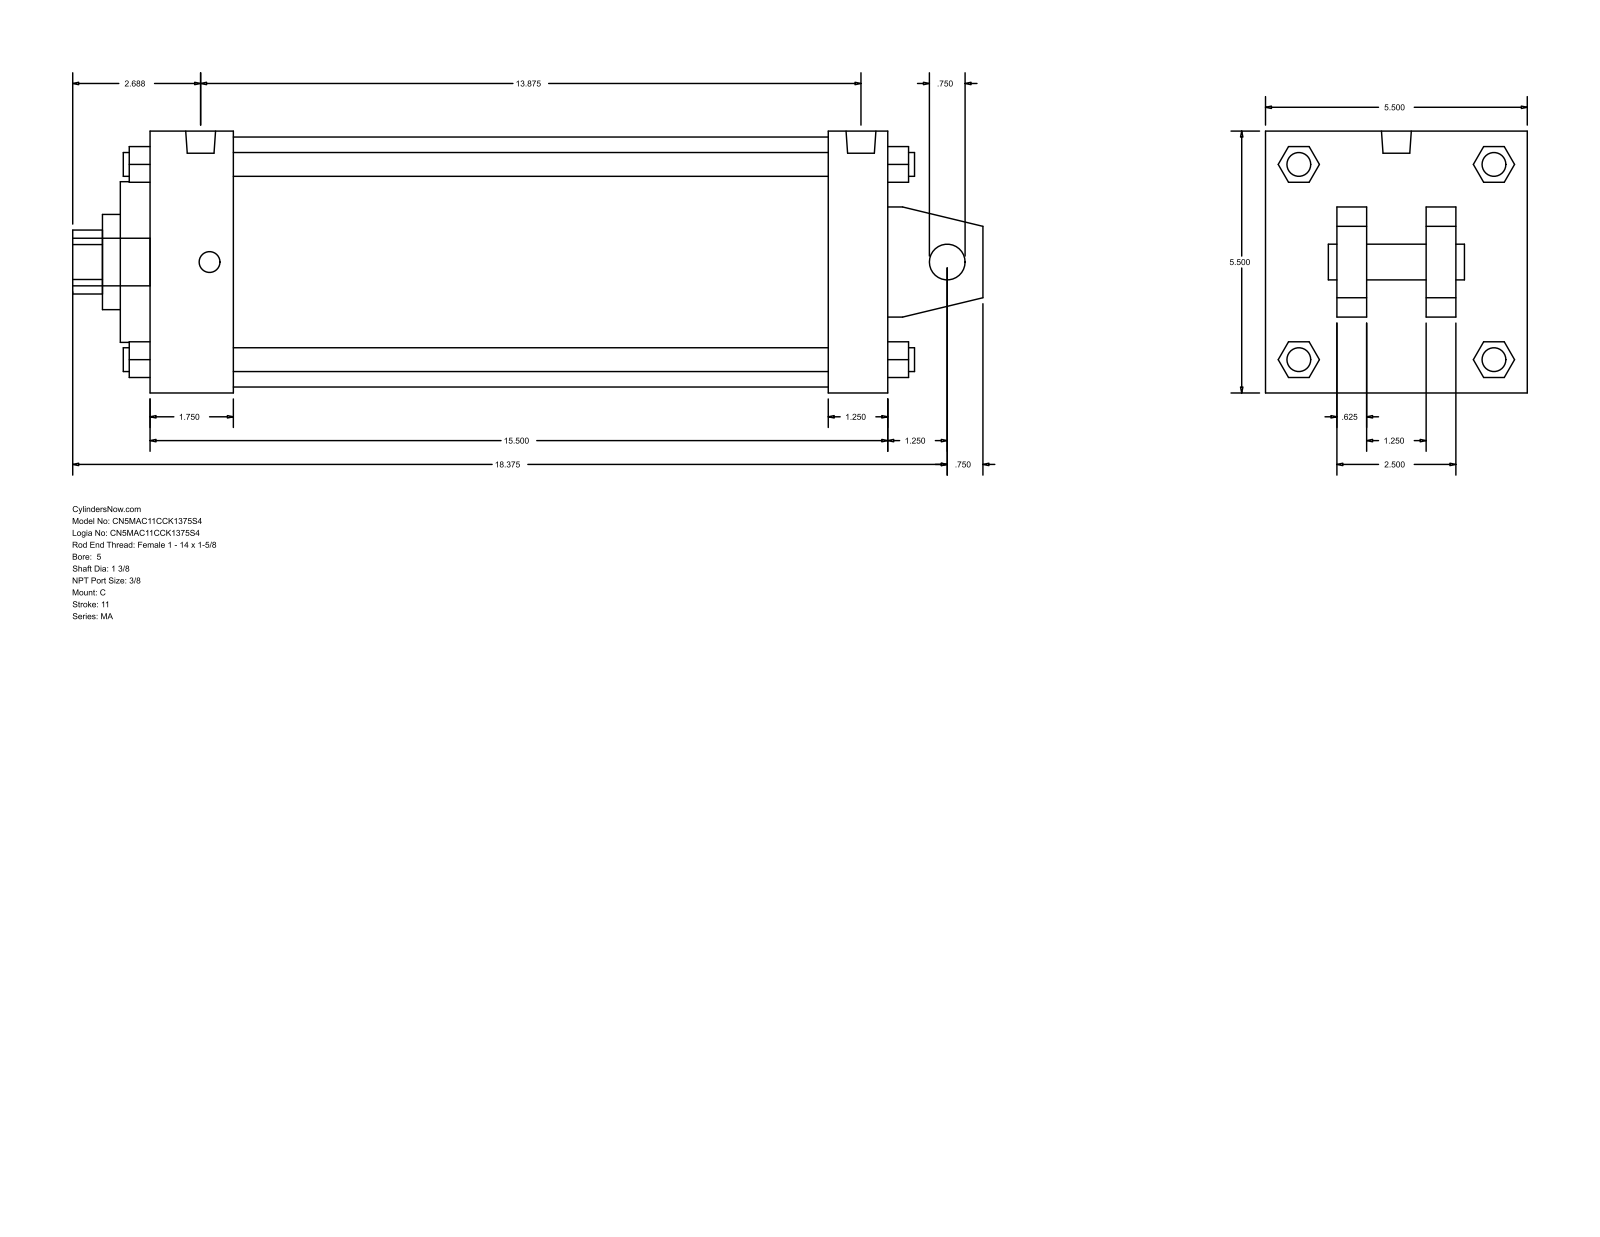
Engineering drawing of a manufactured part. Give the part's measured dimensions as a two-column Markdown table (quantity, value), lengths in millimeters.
| quantity | value |
| --- | --- |
| part name | MA_C__0500_1.375 |
| STEP written by | GSSL Pune (CONFIG_CONTROL_DESIGN) |
| units | millimeters |
| bodies | 0 solids, 141 faces (109 planar, 32 cylindrical, 0 other) |
| overall size | 485.77 × 139.7 × 139.7 |
| round holes (diameter × count) | 19.05 × 1, 34.92 × 1, 50.8 × 1, 85.72 × 1, 133.35 × 1 |
| round bosses / shafts (diameter × count) | 12.7 × 4, 11.11 × 4, 15.93 × 2, 25.4 × 1 |
| partial cylindrical surfaces (radius × count) | 17.06 × 1 |
| main face-to-face distances | 139.7, 393.71, 15.87, 361.96, 31.75, 44.45, 317.51, 349.26, 38.1, 101.6 |
